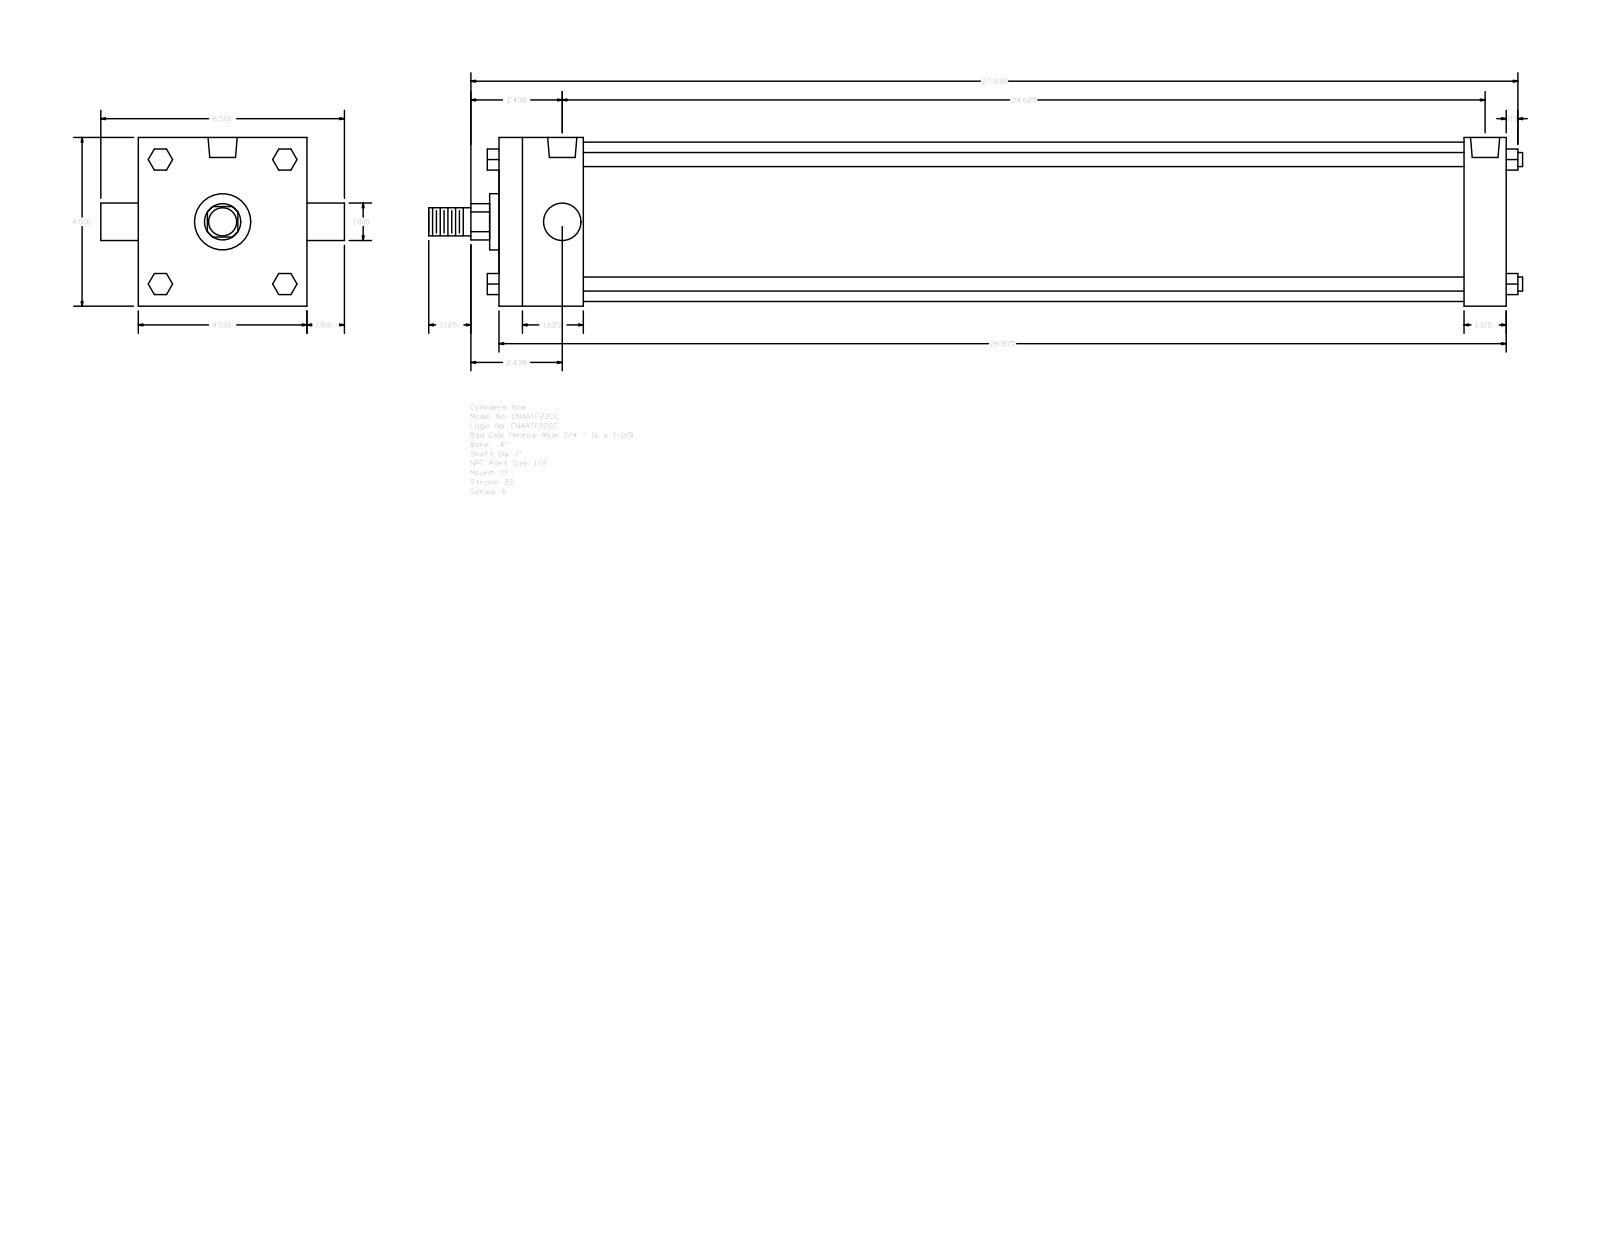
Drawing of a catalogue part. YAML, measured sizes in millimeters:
part_name: "A_TF__0400_1"
step_written_by: "GSSL Pune (CONFIG_CONTROL_DESIGN)"
units: millimeters
bodies: {solids: 0, faces: 120, planar: 92, cylindrical: 28, other: 0}
overall_size: [741.36, 165.1, 114.3]
round_holes:
  - {diameter: 8.73, count: 3}
  - {diameter: 19.77, count: 2}
round_bosses_or_shafts:
  - {diameter: 9.53, count: 4}
  - {diameter: 25.4, count: 2}
  - {diameter: 107.95, count: 1}
  - {diameter: 38.1, count: 1}
  - {diameter: 19.05, count: 1}
partial_cylinders:
  - {radius: 12.29, count: 1}
face_to_face_distances: [114.3, 682.62, 28.57, 654.05, 57.15, 596.9, 625.47, 14.29, 42.16, 73.03]
hole_center_spacings: [3.18, 622.3, 619.12, 625.48]
